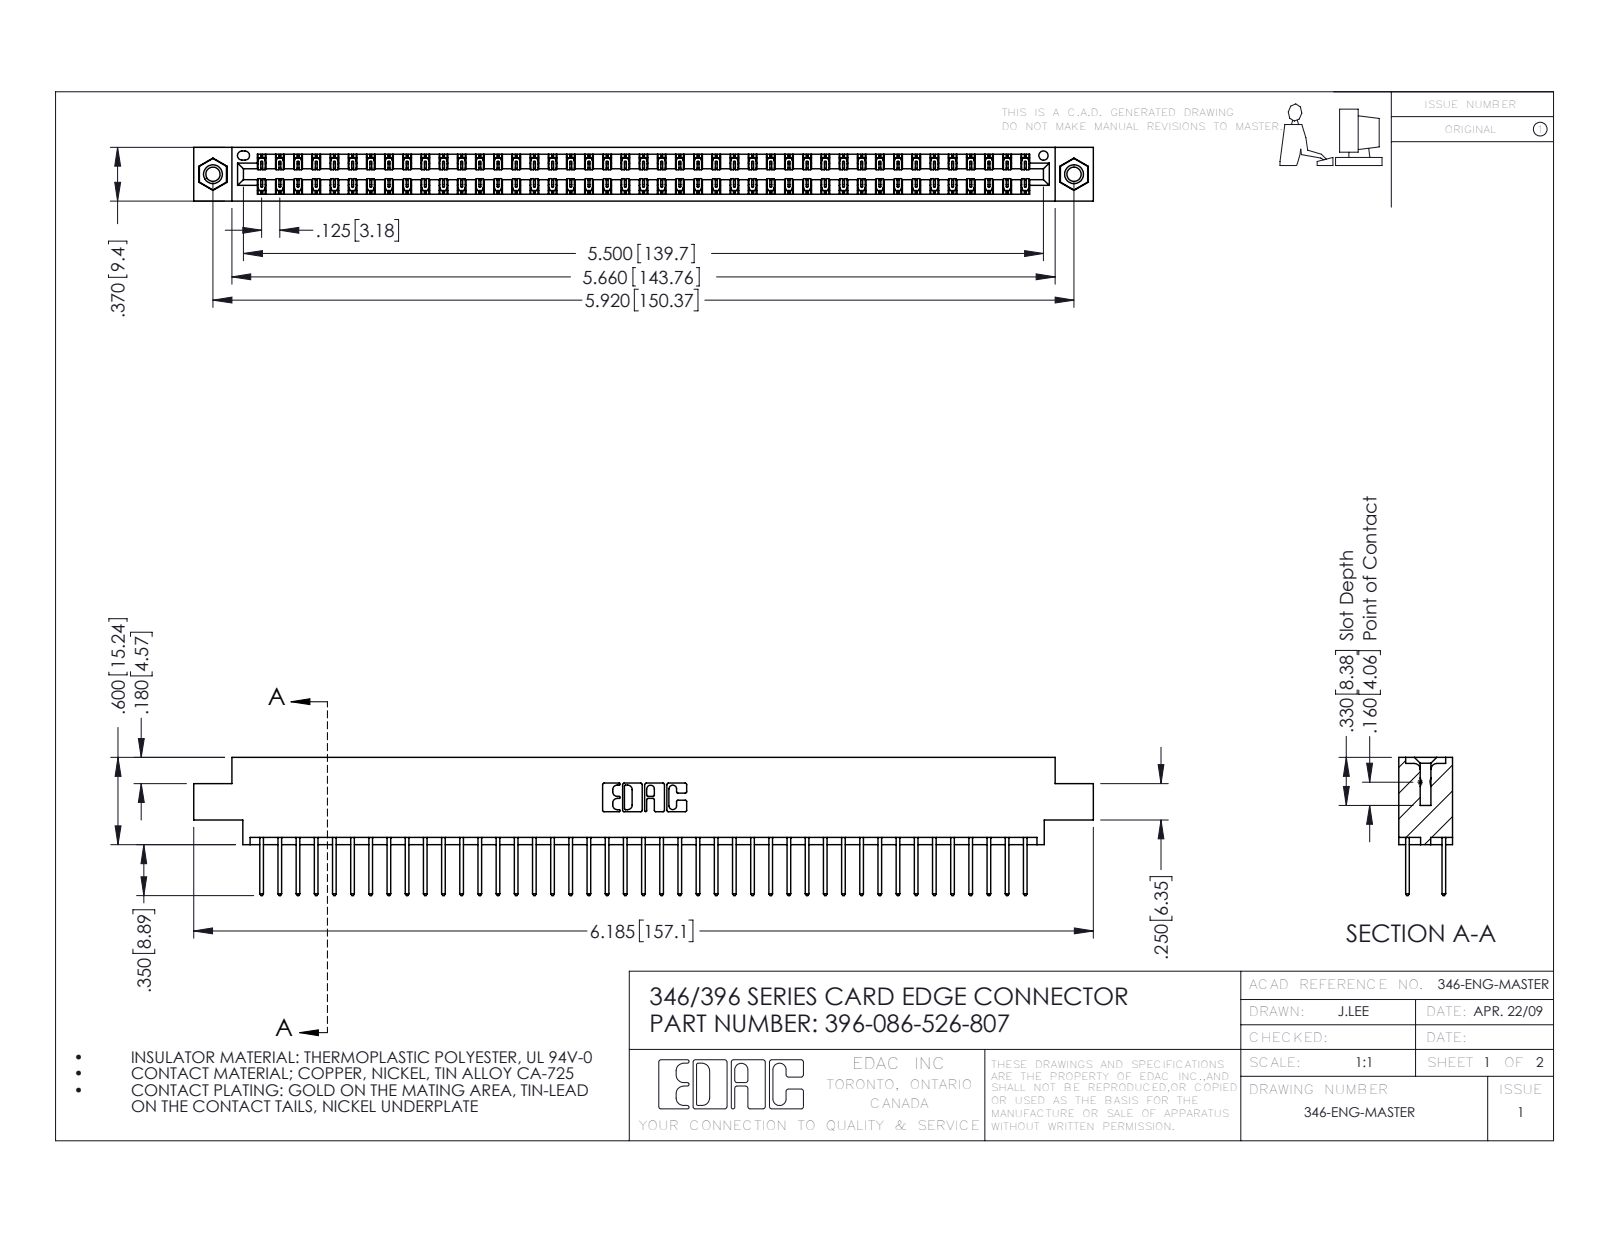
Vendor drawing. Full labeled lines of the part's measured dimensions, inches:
Part name (STEP PRODUCT): 396-086-526-807; 345-292-001_345-293-126; 345-250-001_345-250-005-103; 346 Part_0.170 Offset - 0.156 Dia-TI
STEP written by: SolidWorks 2016 (CONFIG_CONTROL_DESIGN)
Units: inches
Bodies: 89 solids, 4658 faces (3122 planar, 1520 cylindrical, 16 other)
Overall size (bounding box): 6.185 × 0.95 × 0.37
Volume: 0.934 in³ · Surface area: 33.93 in²
Round holes (diameter × count): ⌀0.098 ×2, ⌀0.125 ×2, ⌀0.156 ×2, ⌀0.064 ×1
Round bosses / shafts (diameter × count): ⌀0.155 ×2
Partial cylindrical surfaces — rounded edges, fillets, slot ends (radius × count): R0.006 ×129, R0.01 ×86, R0.01 ×22, R0.007 ×6, R0.031 ×6, R0.026 ×3, R0.014 ×2, R0.022 ×2
Main face-to-face distances: 0.048, 0.322, 0.25, 0.37, 0.072, 0.298, 0.025, 0.275, 0.222, 0.148
Hole centre spacings: 0.246, 5.711, 5.92
